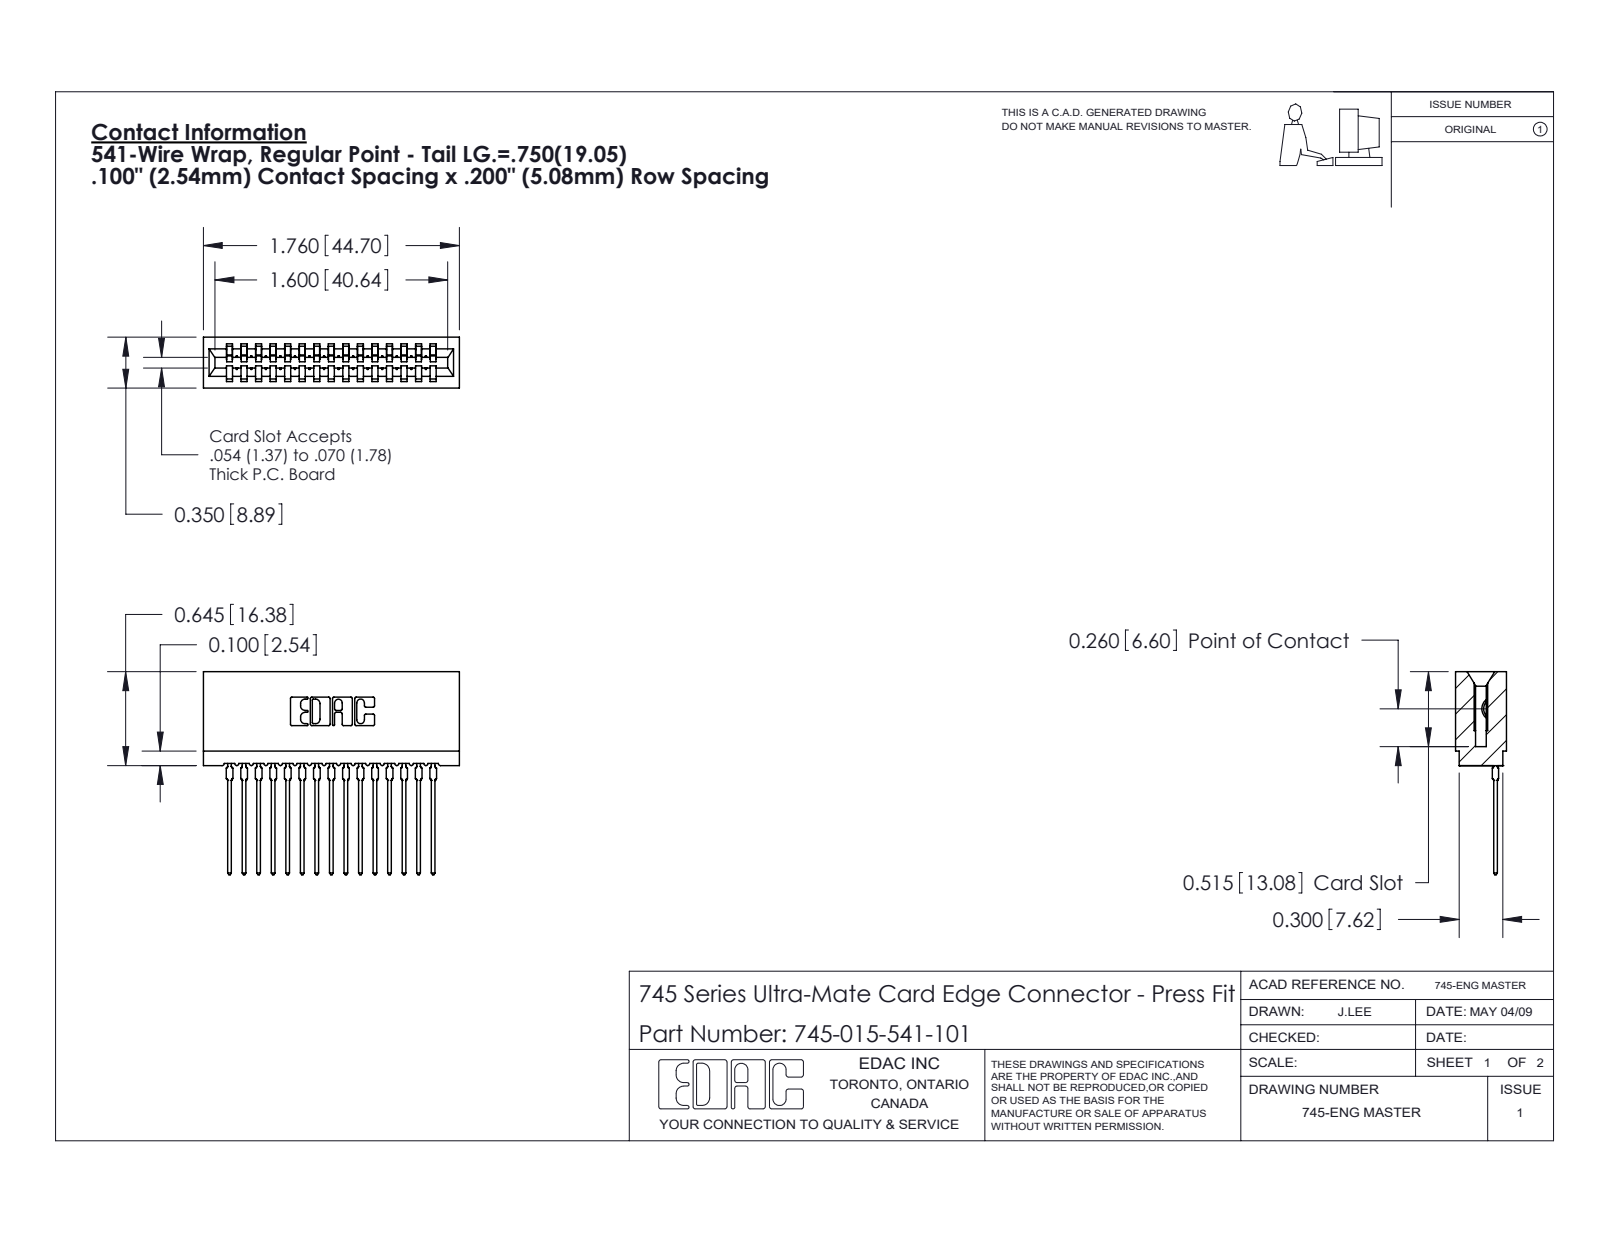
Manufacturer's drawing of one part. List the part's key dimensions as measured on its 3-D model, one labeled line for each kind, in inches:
Part name (STEP PRODUCT): 745 Part_Insulator Option - 01; 745-015-541-101; 745-292-001_541
STEP written by: SolidWorks 2020 (CONFIG_CONTROL_DESIGN)
Units: inches
Bodies: 16 solids, 1775 faces (1060 planar, 325 cylindrical, 390 other)
Overall size (bounding box): 1.76 × 1.396 × 0.35
Volume: 0.251 in³ · Surface area: 11.52 in²
Partial cylindrical surfaces — rounded edges, fillets, slot ends (radius × count): R0.015 ×30, R0.021 ×30, R0.01 ×22, R0.007 ×6, R0.031 ×6, R0.005 ×4, R0.011 ×4, R0.026 ×3
Main face-to-face distances: 0.1, 0.2, 0.3, 0.4, 0.35, 0.5, 0.6, 0.7, 0.138, 0.212
